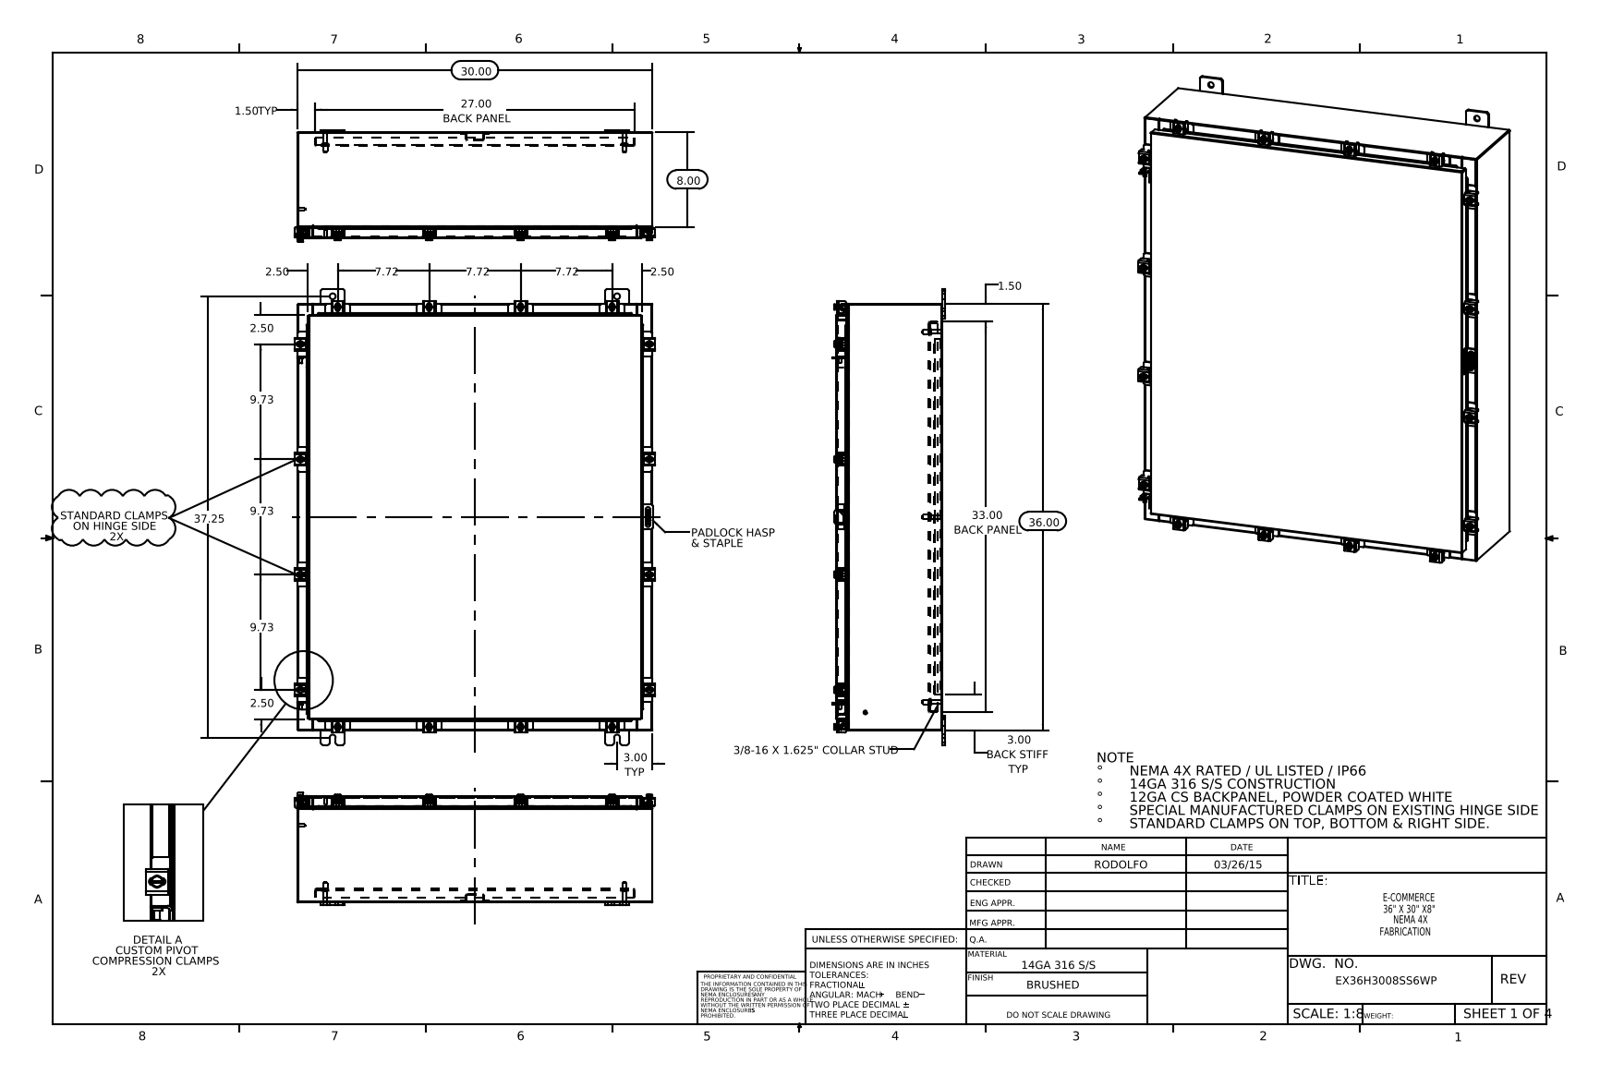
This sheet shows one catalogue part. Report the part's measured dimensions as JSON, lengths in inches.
{"part_name": "N-WMT04X30402202210-00 22101002; EX36H3008SS6WP Mounting Studs; HW-CLN-NH-20330; 30X10 Clamp Bracket2 (+8 more)", "step_written_by": "SolidWorks 2014 (CONFIG_CONTROL_DESIGN)", "units": "inches", "bodies": {"solids": 104, "faces": 2594, "planar": 1371, "cylindrical": 1011, "other": 212}, "overall_size": [38.5, 30.421, 9.453], "volume_in3": 381.4, "surface_area_in2": 9441, "round_holes": [[0.213, 16], [0.26, 16], [0.5, 10], [0.125, 1], [0.25, 1]], "round_bosses_or_shafts": [[0.5, 16], [0.25, 16], [0.399, 14], [0.625, 6], [0.375, 6], [0.33, 6], [0.315, 2], [0.236, 2]], "partial_cylinders_radius": [[0.06, 70], [0.141, 32], [0.013, 30], [0.12, 30], [0.088, 26], [0.19, 24], [0.09, 22], [0.05, 21]], "face_to_face_distances": [0.075, 8.9, 8.826, 8.975, 0.104, 1, 1.075, 7.826, 7.9, 1.179], "hole_center_spacings": [31.017, 2.347, 4.44, 5.299, 9.73, 10.964, 13.241, 14.744]}
